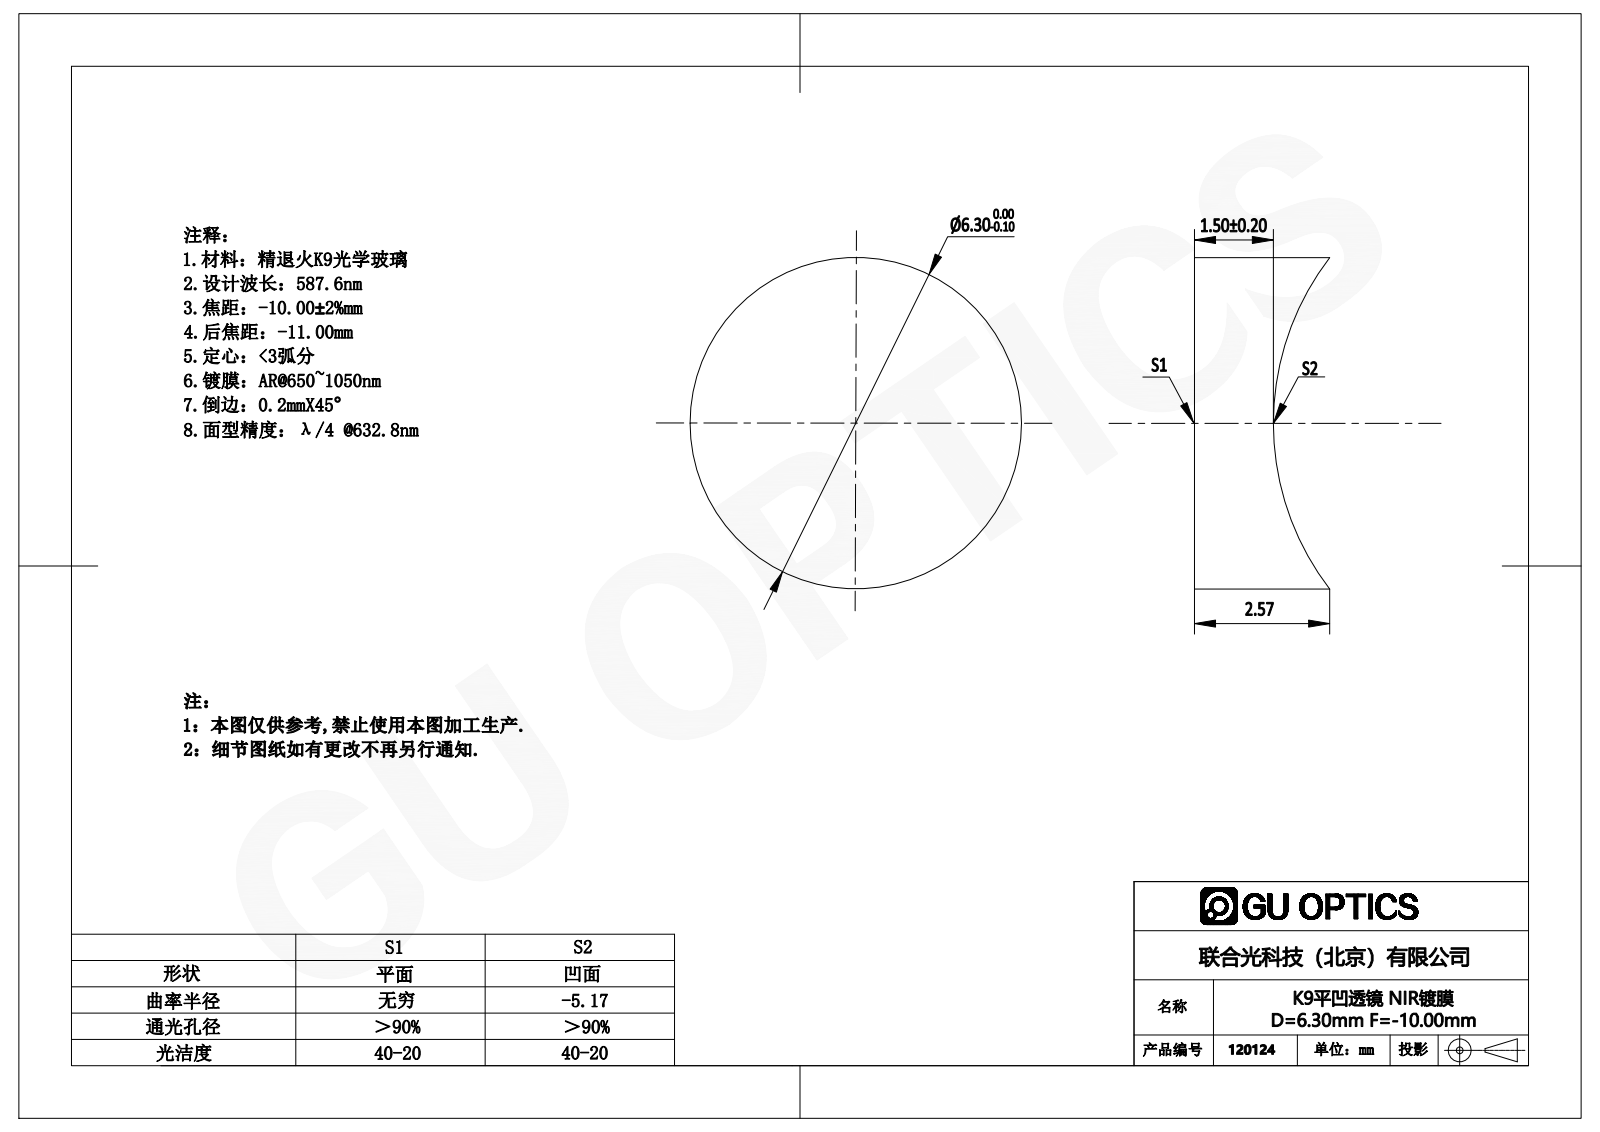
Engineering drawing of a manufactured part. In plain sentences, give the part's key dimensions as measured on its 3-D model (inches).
The part is named "120124". Its 3-D file was written by "SolidWorks 2016 (AUTOMOTIVE_DESIGN)". It is 1 solid with 5 faces: 1 planar, 2 cylindrical and 2 other. Overall it measures 0.248 by 0.248 by 0.101 inches. Its volume is 0.004 cubic inches and its surface area 0.181 square inches. Round bosses or shafts: 1 of diameter 0.248.
